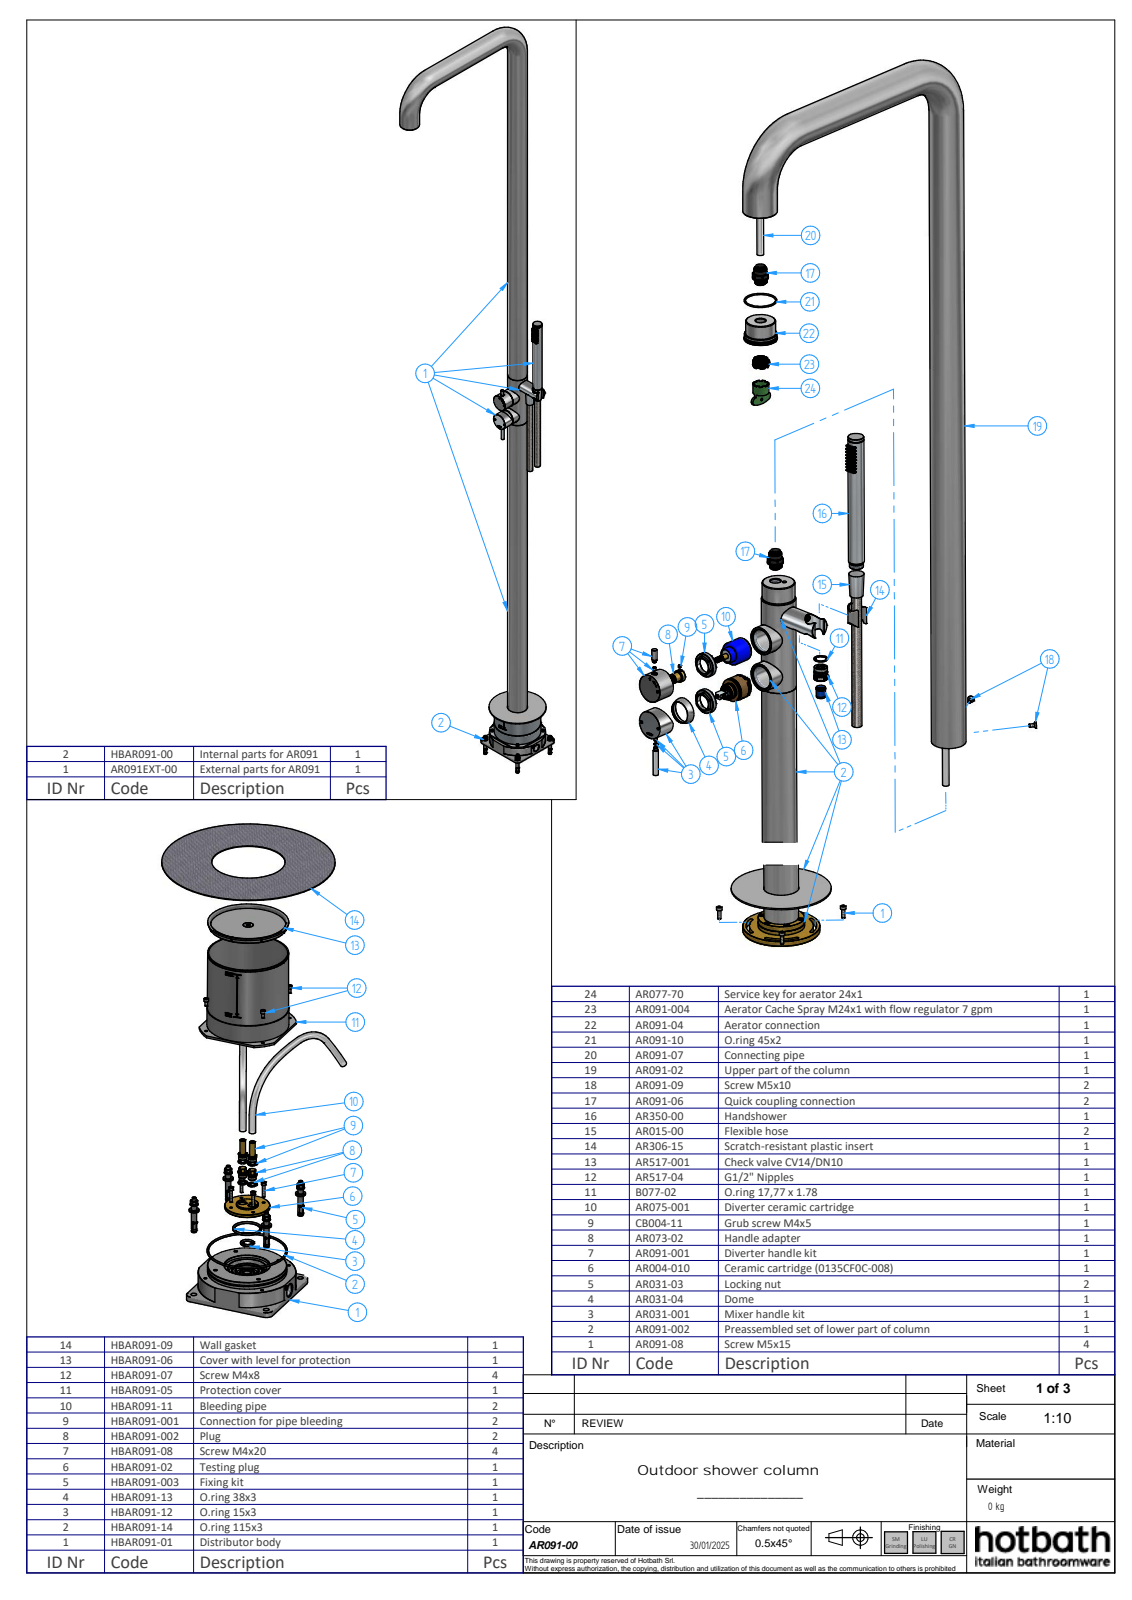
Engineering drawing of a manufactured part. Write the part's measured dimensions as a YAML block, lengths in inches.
part_name: "AR091EXT-00; ZNTB136AC; set flangia_oa_0; ZNRS052AC (+8 more)"
step_written_by: "Solid Edge (AUTOMOTIVE_DESIGN)"
units: inches
bodies: {solids: 63, faces: 4657, planar: 2881, cylindrical: 349, other: 1427}
overall_size: [88.858, 19.724, 6.339]
volume: 81.83
surface_area: 1579
round_holes:
  - {diameter: 0.098, count: 36}
  - {diameter: 0.315, count: 7}
  - {diameter: 0.197, count: 5}
  - {diameter: 0.394, count: 4}
  - {diameter: 0.354, count: 3}
  - {diameter: 0.591, count: 3}
  - {diameter: 0.163, count: 2}
  - {diameter: 0.169, count: 2}
  - {diameter: 0.236, count: 2}
  - {diameter: 0.323, count: 2}
  - {diameter: 0.413, count: 2}
  - {diameter: 0.433, count: 2}
round_bosses_or_shafts:
  - {diameter: 0.197, count: 5}
  - {diameter: 2.047, count: 3}
  - {diameter: 1.89, count: 2}
  - {diameter: 1.693, count: 2}
  - {diameter: 1.614, count: 2}
  - {diameter: 1.555, count: 2}
  - {diameter: 0.825, count: 2}
  - {diameter: 0.236, count: 2}
partial_cylinders:
  - {radius: 0.02, count: 12}
  - {radius: 0.506, count: 4}
  - {radius: 0.009, count: 2}
  - {radius: 0.015, count: 2}
  - {radius: 0.017, count: 2}
  - {radius: 0.027, count: 2}
  - {radius: 0.039, count: 2}
  - {radius: 0.079, count: 2}
face_to_face_distances: [0.079, 81.689, 81.61, 36.098, 36.019, 45.591, 43.185, 43.106, 7.087, 38.504]
hole_center_spacings: [0.197, 0.269, 0.394, 0.435, 0.591, 0.619, 0.787, 0.809]
